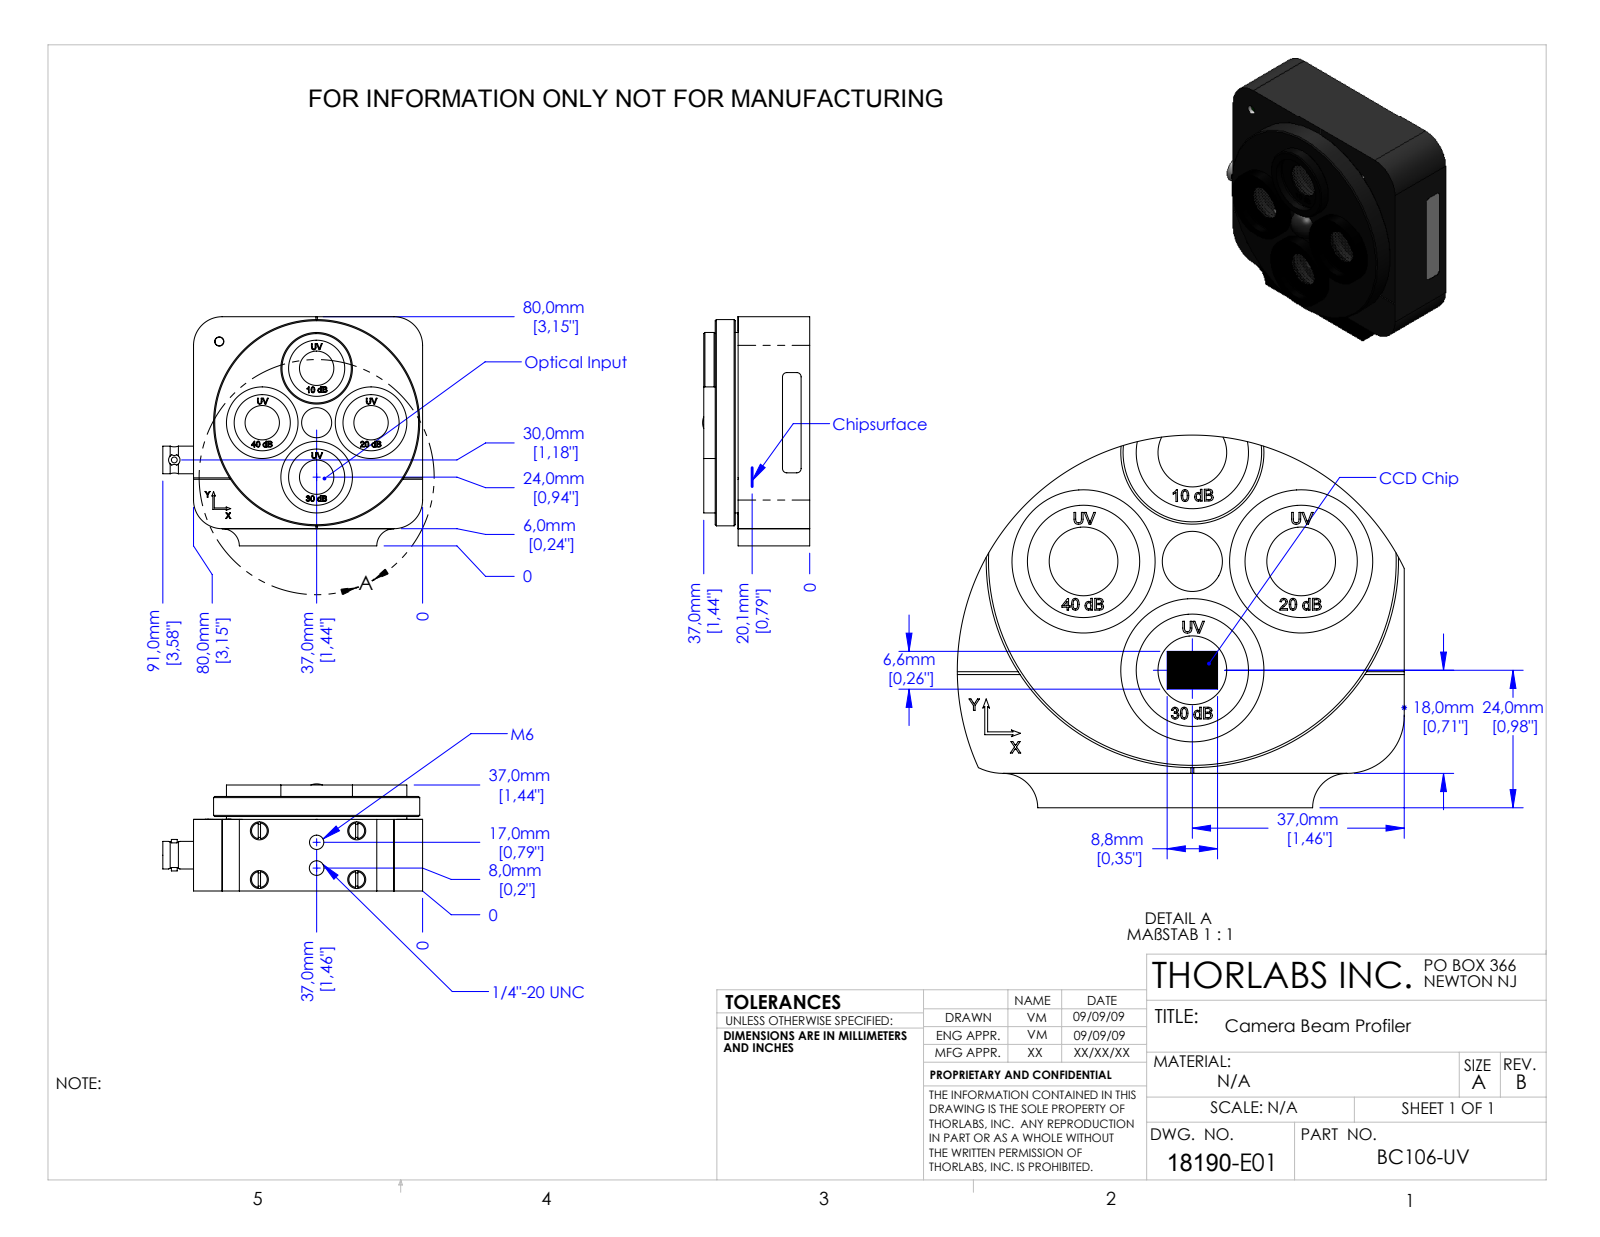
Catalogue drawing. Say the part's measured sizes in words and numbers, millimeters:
The part is named "18190-E0W". Its 3-D file was written by "SolidWorks 2012 (CONFIG_CONTROL_DESIGN)". It is 0 solids with 425 faces: 279 planar, 115 cylindrical and 31 other. Overall it measures 90.72 by 80 by 37.4 millimeters. Round holes: 4 of diameter 1.6, 4 of diameter 12, 4 of diameter 19.61, 4 of diameter 20.61, 1 of diameter 3.2, 1 of diameter 5, 1 of diameter 5.11, 1 of diameter 8.35, 1 of diameter 12.7. Round bosses or shafts: 4 of diameter 25, 4 of diameter 5.5, 1 of diameter 72, 1 of diameter 12.6, 1 of diameter 10.5, 1 of diameter 9.64, 1 of diameter 2.03, 1 of diameter 0.28. Partial cylindrical surfaces (rounded edges, fillets, slot ends): 8 of radius 0.3, 7 of radius 0.7, 6 of radius 9, 4 of radius 1, 4 of radius 1.5, 4 of radius 10, 2 of radius 6, 1 of radius 2. The main face-to-face distances are 32.7, 8, 24.7, 80, 5, 13, 19.7, 23.2, 31.2, 18.2. The hole center spacings are 26.87, 23.33, 26.2, 38, 48.76, 50.2, 9, 19.24.
